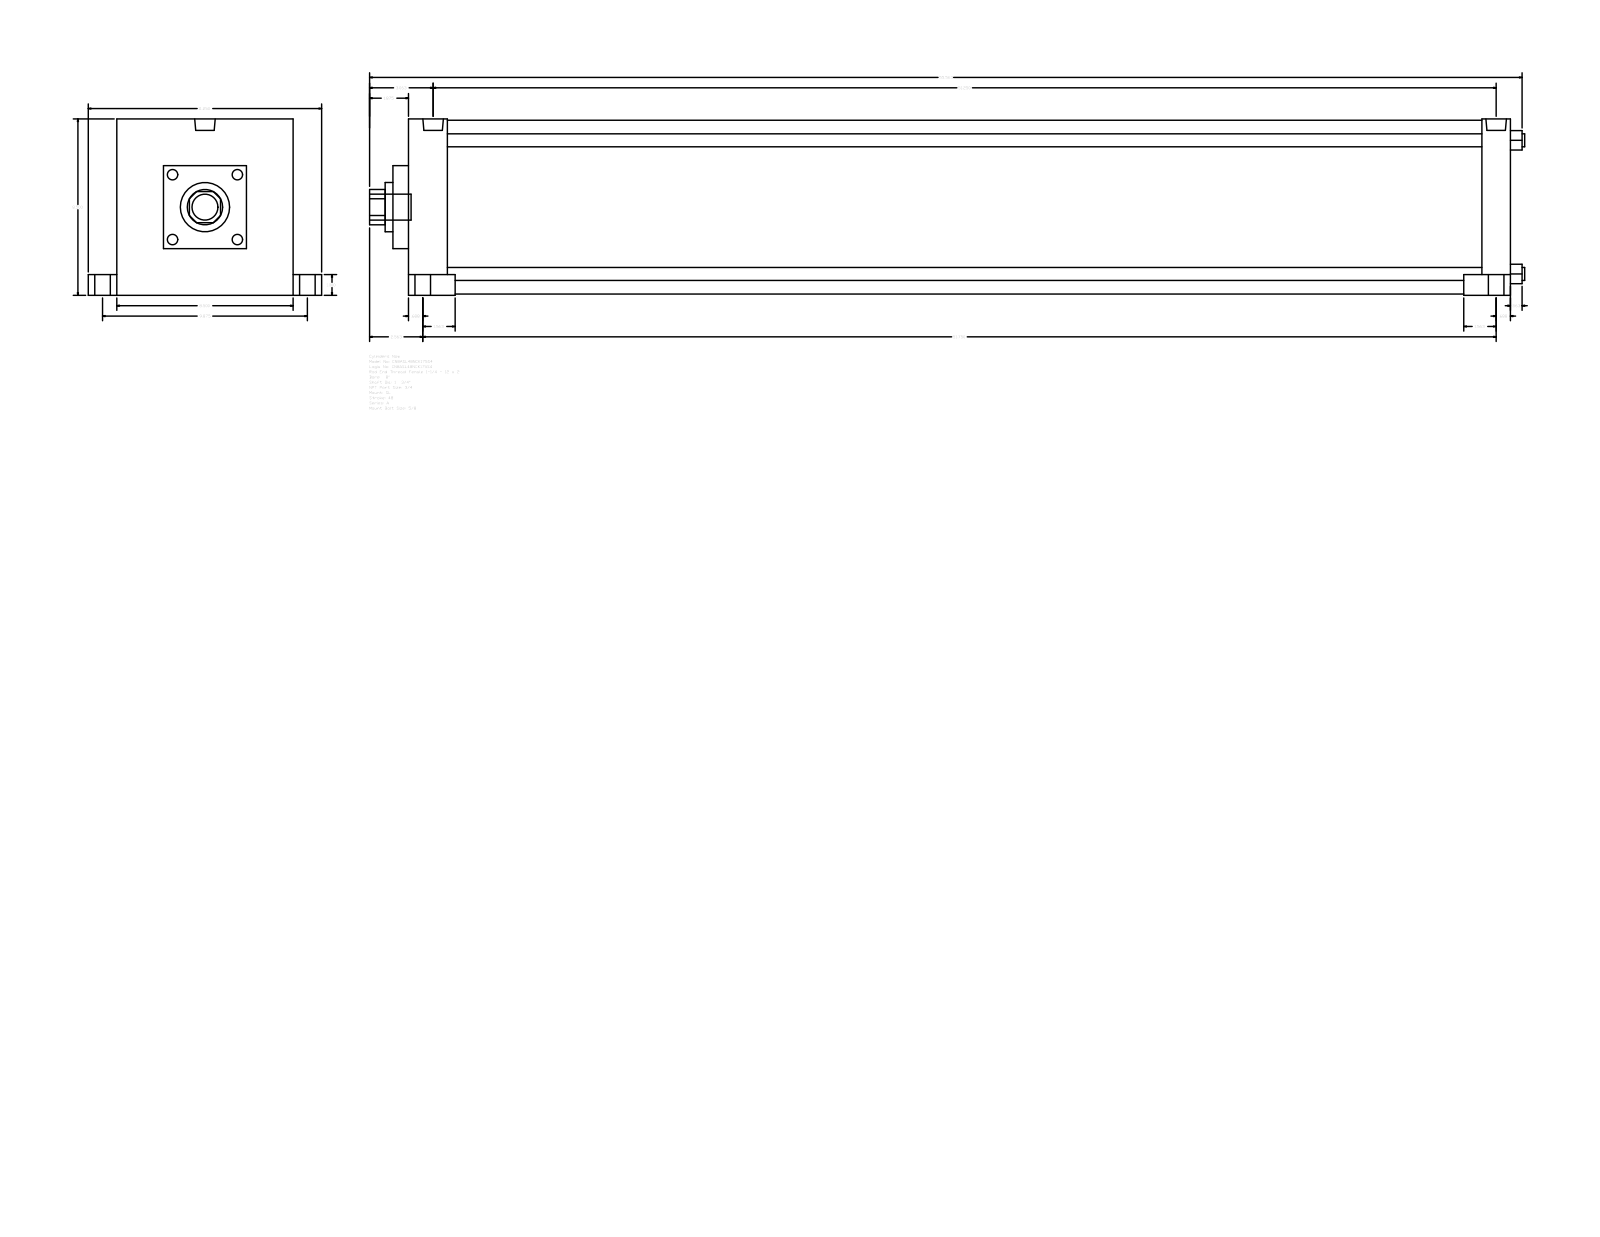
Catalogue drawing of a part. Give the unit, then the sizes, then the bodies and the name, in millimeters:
Units: millimetres
Overall size (bounding box): 1414.46 × 285.75 × 215.9
Round holes (diameter × count): ⌀15.88 ×4, ⌀44.45 ×1, ⌀60.33 ×1, ⌀212.72 ×1
Round bosses / shafts (diameter × count): ⌀25.4 ×4, ⌀19.05 ×4, ⌀15.08 ×4, ⌀25.12 ×2, ⌀31.75 ×1
Partial cylindrical surfaces — rounded edges, fillets, slot ends (radius × count): R21.63 ×1
Main face-to-face distances: 1349.38, 215.9, 34.92, 47.63, 1301.75, 1314.46, 1266.83, 57.15, 19.05, 158.75
Hole centre spacings: 115.67, 163.58, 231.34
Bodies: 0 solids, 117 faces (85 planar, 32 cylindrical, 0 other)
Part name (STEP PRODUCT): A_SL__0800_1.75
STEP written by: GSSL Pune (CONFIG_CONTROL_DESIGN)
